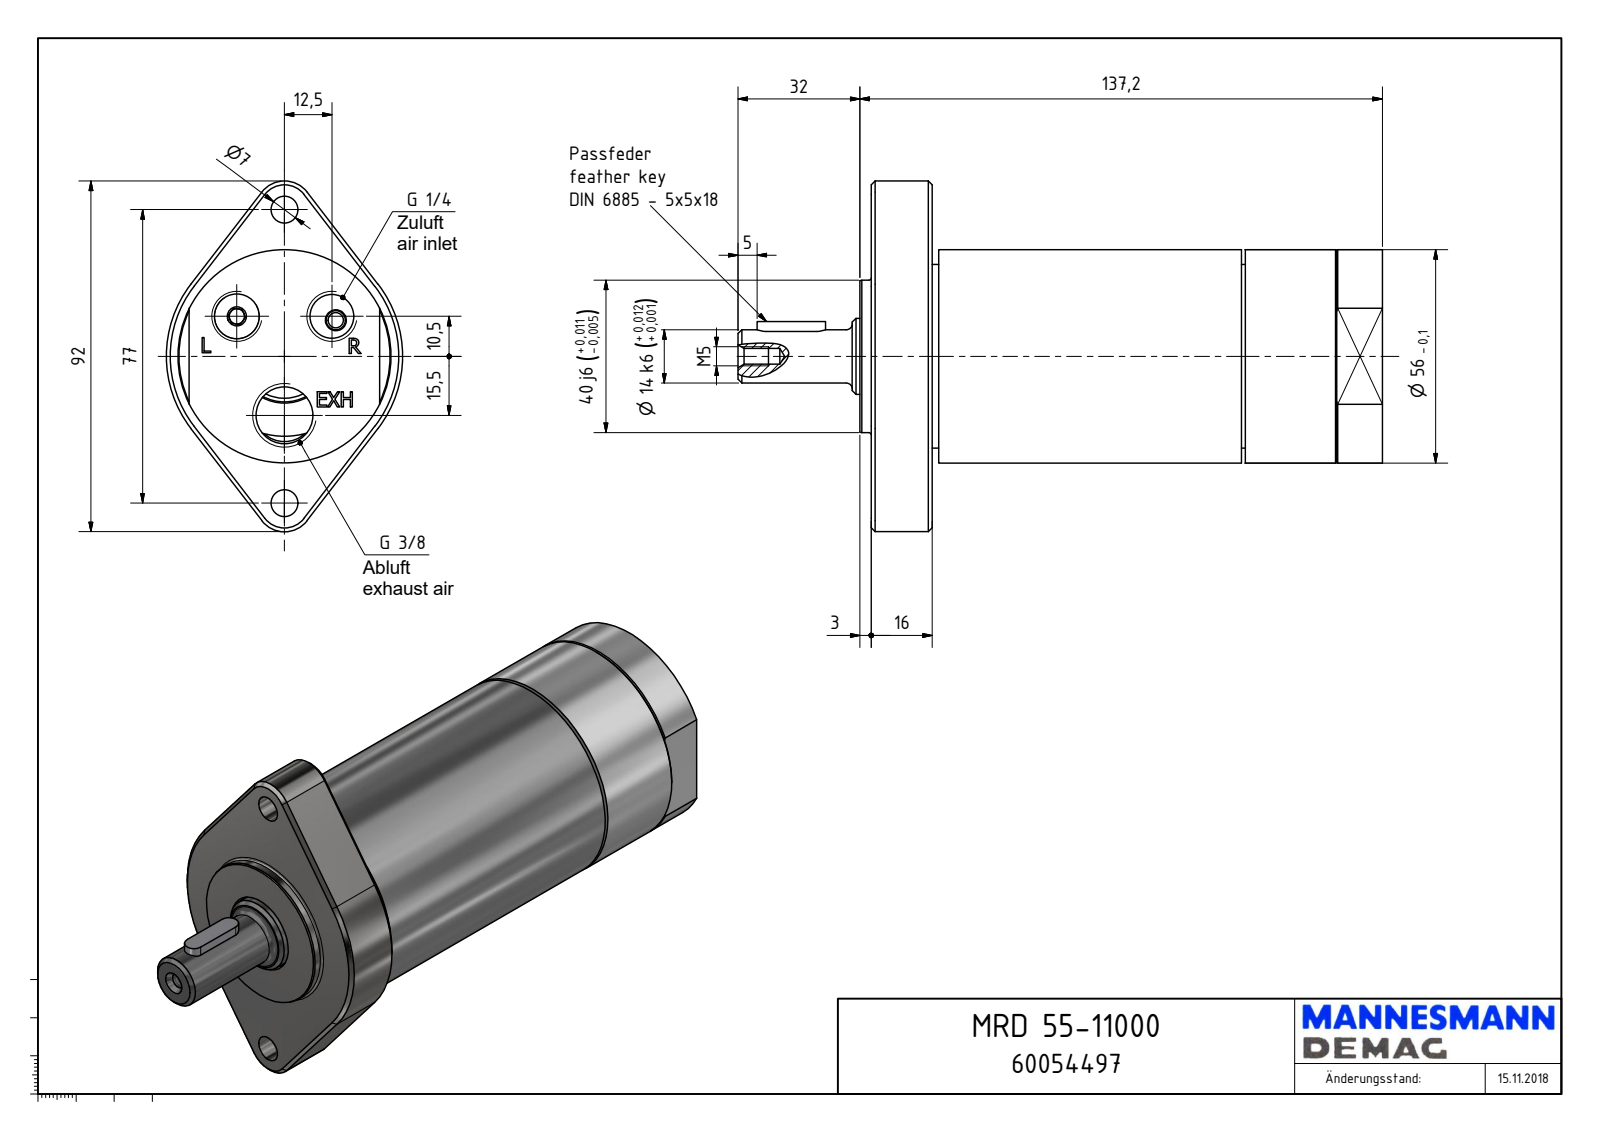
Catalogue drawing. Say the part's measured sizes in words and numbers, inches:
The part is named "MRD 55-11000 F77_60054497". Its 3-D file was written by "Autodesk Inventor 2018 (AUTOMOTIVE_DESIGN)". It is 1 solid with 194 faces: 111 planar, 30 cylindrical and 53 other. Overall it measures 6.661 by 3.622 by 2.441 inches. Its volume is 21.47 cubic inches and its surface area 62.01 square inches. Round holes: 2 of diameter 0.276, 1 of diameter 0.157, 1 of diameter 0.163, 1 of diameter 0.451, 1 of diameter 0.589, 1 of diameter 0.827, 1 of diameter 0.837, 1 of diameter 0.927, 1 of diameter 1.024, 1 of diameter 1.905. Round bosses or shafts: 1 of diameter 2.205, 1 of diameter 1.897, 1 of diameter 1.575, 1 of diameter 0.785, 1 of diameter 0.551. Partial cylindrical surfaces (rounded edges, fillets, slot ends): 2 of radius 0.098, 2 of radius 0.295, 1 of radius 1.22. The main face-to-face distances are 5.283, 0.63, 4.654, 0.118, 0.748, 5.402, 0.815, 0.697, 0.067, 4.587. The hole center spacings are 0.643, 1.136, 1.207, 1.516, 1.991, 0.61, 0.906, 0.984.
